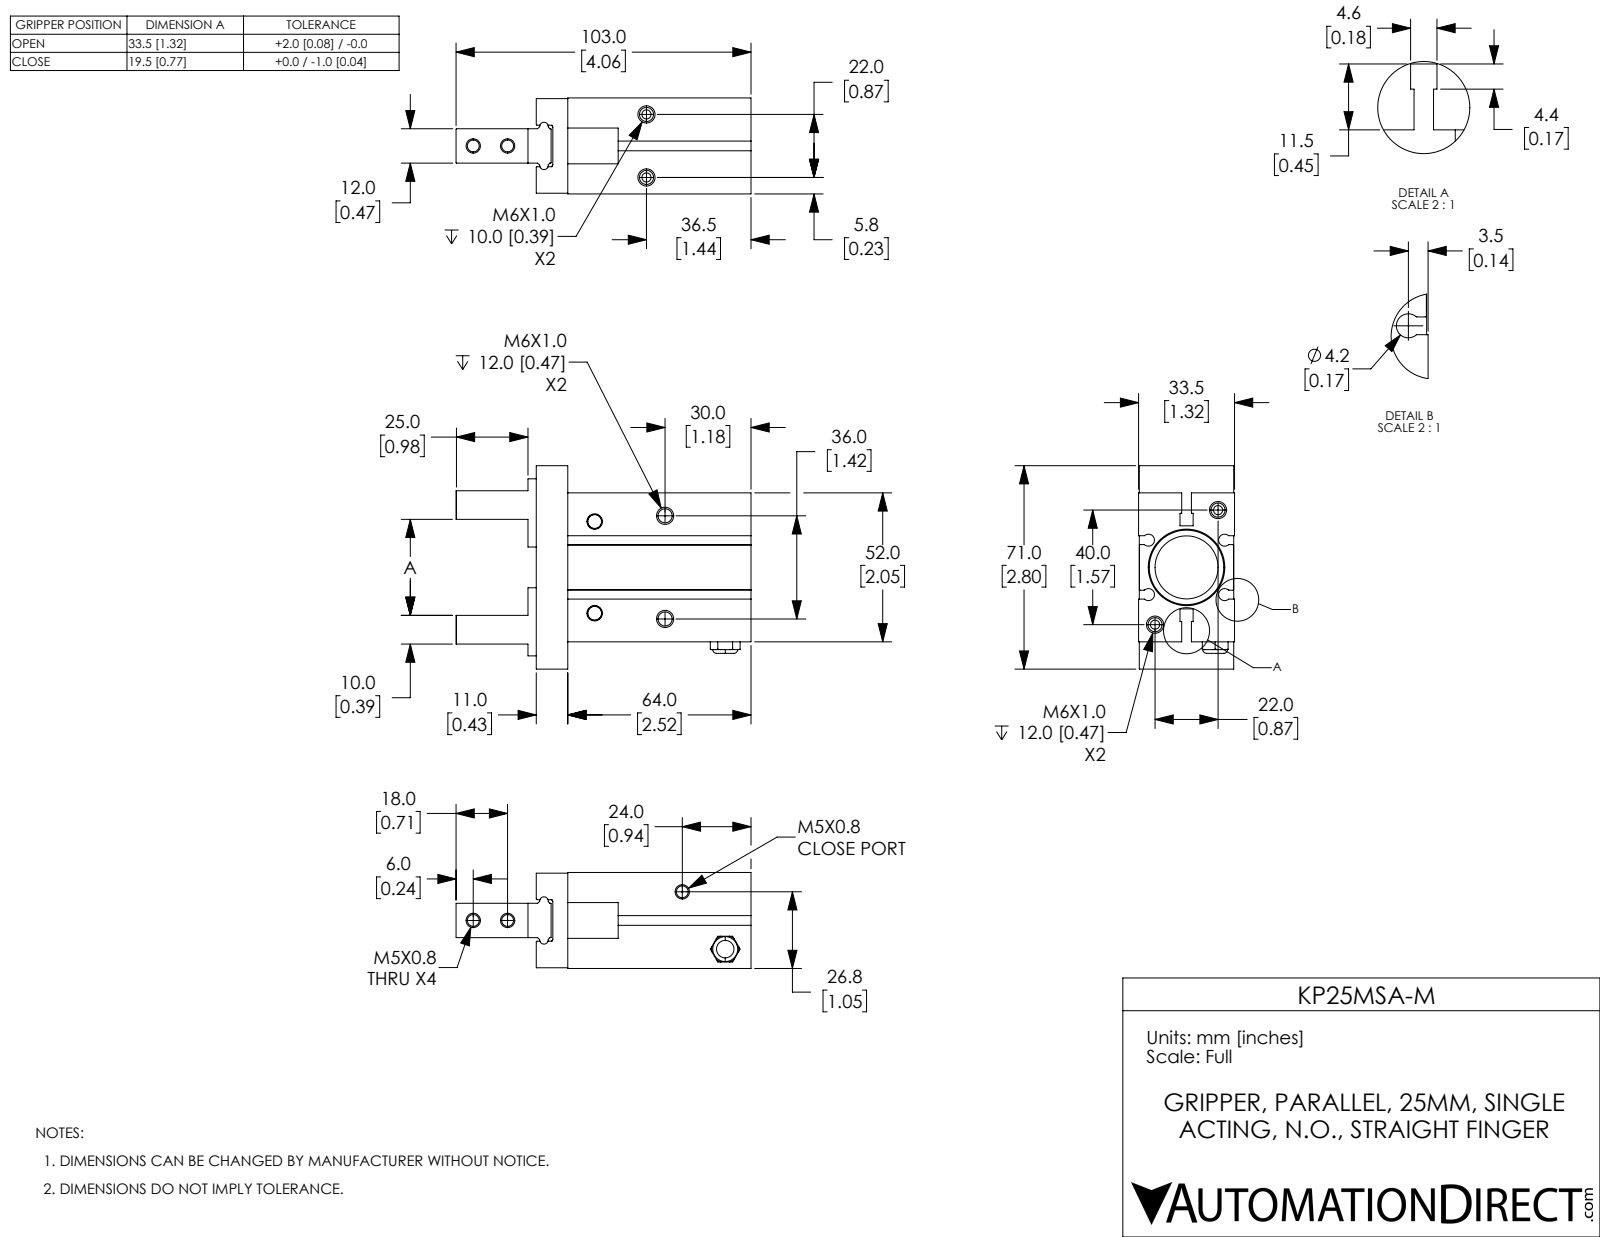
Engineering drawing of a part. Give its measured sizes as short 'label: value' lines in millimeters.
name: KP25MSA-M; KP25MSA-M-3; KP25MSA-M-2; KP25MSA-M-1
written by: SolidWorks 2017 (CONFIG_CONTROL_DESIGN)
unit: mm
bodies: 3 solids, 265 faces (129 planar, 66 cylindrical, 70 other)
size: 103 × 71 × 33.5
volume: 117 033 mm³; area: 33 373 mm²
holes: 4× ⌀4.13, 4× ⌀4.92, 2× ⌀0.5, 2× ⌀4.92, 2× ⌀6.02, 1× ⌀6.1, 1× ⌀22, 1× ⌀26
rounds: 8× R0.2, 4× R2.1, 2× R0.5, 2× R1.5
face distances: 10.5, 22.75, 33.2, 33.5, 23, 10.2, 22.7, 12.25, 22.45, 52
hole spacings: 22.83, 49.73, 61.49, 12, 12.54, 22, 24.44, 25
